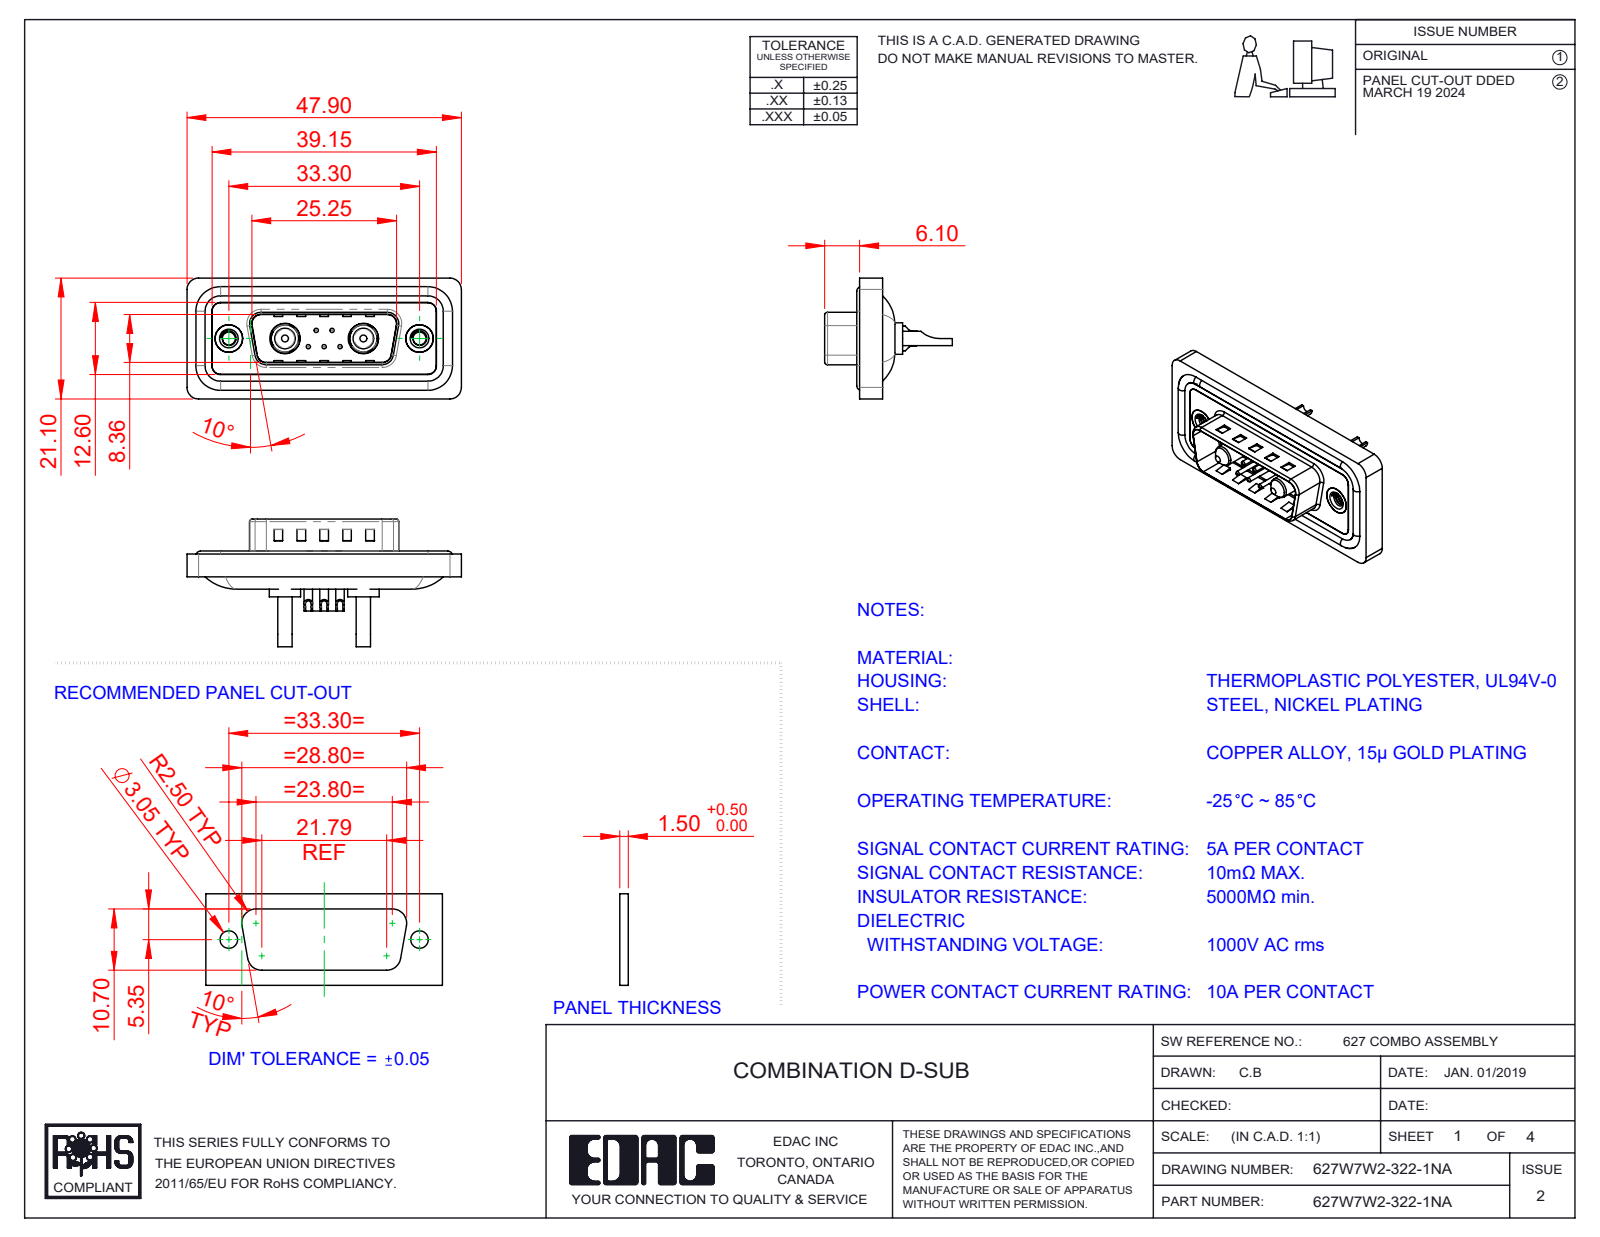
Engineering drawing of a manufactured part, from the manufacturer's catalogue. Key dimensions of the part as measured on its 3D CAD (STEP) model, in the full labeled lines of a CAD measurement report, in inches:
Part name (STEP PRODUCT): 627Combo Threaded Rivet_A; 627Combo Shell Front_15 Contacts; 627Combo Contact Row 2_22; 627Combo Contact Row 1_22 (+5 more)
STEP written by: SolidWorks 2023 (CONFIG_CONTROL_DESIGN)
Units: inches
Bodies: 16 solids, 720 faces (246 planar, 310 cylindrical, 164 other)
Overall size (bounding box): 1.886 × 0.878 × 0.831
Volume: 0.337 in³ · Surface area: 13.84 in²
Round holes (diameter × count): ⌀0.03 ×5, ⌀0.039 ×5, ⌀0.063 ×5, ⌀0.079 ×5, ⌀0.067 ×2, ⌀0.089 ×2, ⌀0.157 ×2, ⌀0.189 ×2, ⌀0.191 ×2, ⌀0.197 ×2, ⌀0.209 ×2
Round bosses / shafts (diameter × count): ⌀0.059 ×5, ⌀0.063 ×4, ⌀0.217 ×2, ⌀0.205 ×2, ⌀0.193 ×2, ⌀0.187 ×2, ⌀0.148 ×2, ⌀0.142 ×2
Partial cylindrical surfaces — rounded edges, fillets, slot ends (radius × count): R0.059 ×26, R0.079 ×20, R0.02 ×8, R0.063 ×8, R0.039 ×6, R0.01 ×4, R0.024 ×4, R0.026 ×4
Main face-to-face distances: 0.016, 0.043, 0.059, 0.063, 0.02, 0.122, 0.114, 0.157, 0.032, 0.377
Hole centre spacings: 0.124, 0.109, 0.386, 0.925, 0.17, 0.17, 0.198, 0.198
